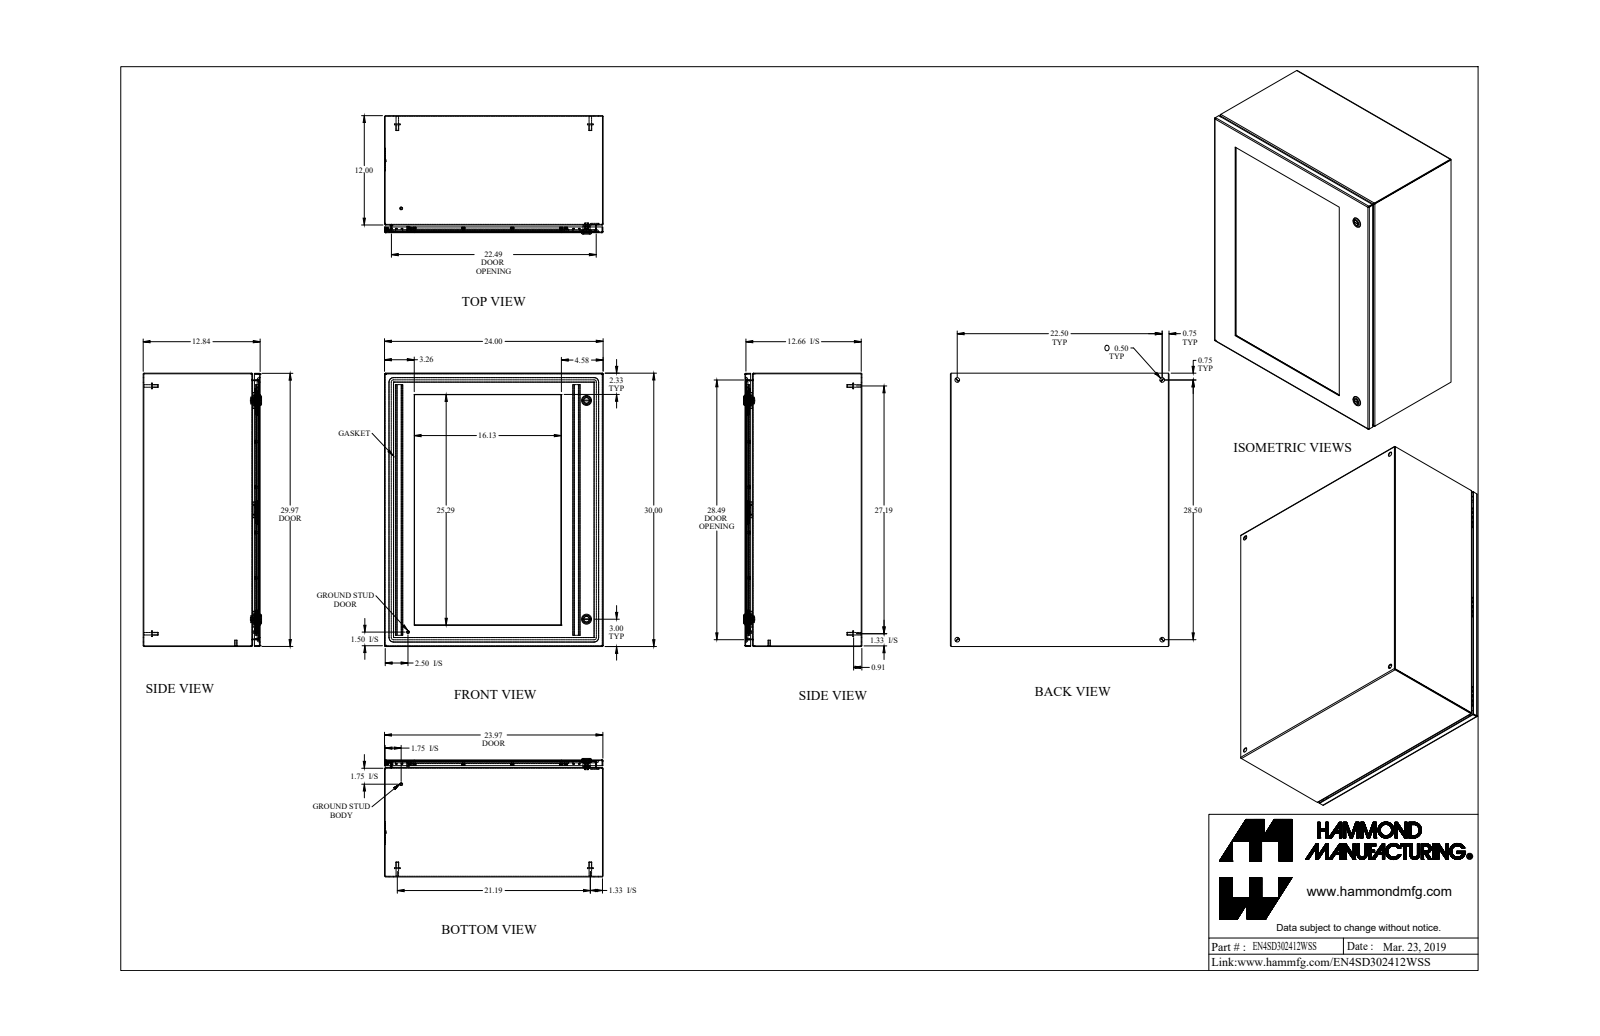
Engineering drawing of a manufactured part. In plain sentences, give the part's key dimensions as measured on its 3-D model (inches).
The part is named "EN4SD302412WSS". Its 3-D file was written by "SolidWorks 2019 (AUTOMOTIVE_DESIGN)". It is 84 solids with 1631 faces: 830 planar, 505 cylindrical and 296 other. Overall it measures 30 by 24 by 12.997 inches. Its volume is 312.4 cubic inches and its surface area 6 706 square inches. Round holes: 20 of diameter 0.13, 20 of diameter 0.25, 6 of diameter 0.5, 2 of diameter 0.197, 2 of diameter 0.387, 2 of diameter 0.63, 2 of diameter 0.768, 1 of diameter 0.172, 1 of diameter 0.24, 1 of diameter 0.242. Round bosses or shafts: 21 of diameter 0.226, 20 of diameter 0.368, 20 of diameter 0.164, 6 of diameter 0.313, 4 of diameter 0.625, 4 of diameter 0.275, 2 of diameter 1.1, 2 of diameter 0.785. Partial cylindrical surfaces (rounded edges, fillets, slot ends): 14 of radius 0.036, 14 of radius 0.108, 12 of radius 0.01, 12 of radius 0.048, 12 of radius 0.125, 12 of radius 0.312, 6 of radius 0.006, 6 of radius 0.062. The main face-to-face distances are 0.072, 12.765, 12.693, 23.928, 29.928, 12.443, 0.25, 12.515, 23.856, 0.322. The hole center spacings are 9.95, 19.822, 4.975, 5.372, 17.144, 17.852, 26.874, 5.931.
